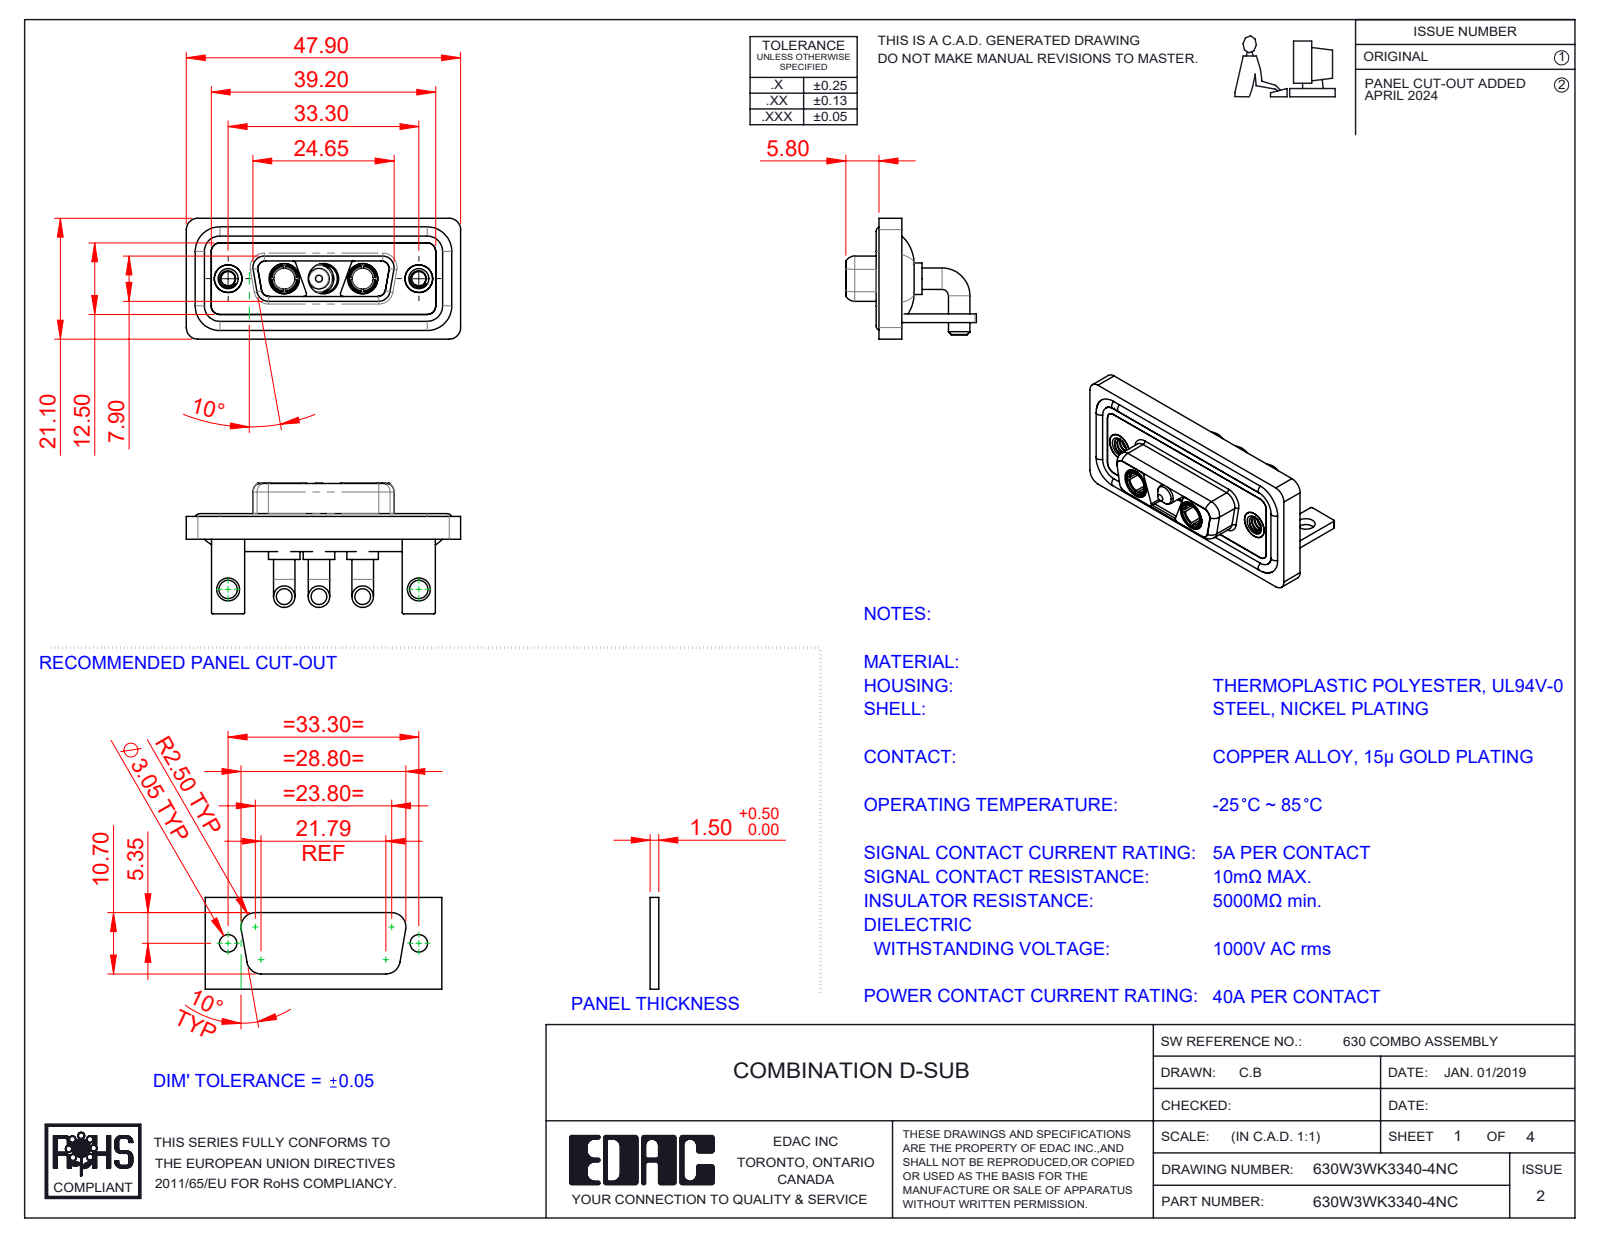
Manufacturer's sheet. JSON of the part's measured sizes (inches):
{"part_name": "630Combo Shell Front_15 Contacts; 630W3WK3340-4NC; 630Combo Waterproof Housing_15 Contacts; 630Combo Threaded Rivet_A (+5 more)", "step_written_by": "SolidWorks 2023 (CONFIG_CONTROL_DESIGN)", "units": "inches", "bodies": {"solids": 15, "faces": 637, "planar": 198, "cylindrical": 286, "other": 153}, "overall_size": [1.886, 0.898, 0.831], "volume_in3": 0.403, "surface_area_in2": 16.44, "round_holes": [[0.191, 5], [0.209, 3], [0.098, 2], [0.126, 2], [0.146, 2], [0.157, 2], [0.159, 2], [0.197, 2]], "round_bosses_or_shafts": [[0.148, 6], [0.063, 4], [0.217, 3], [0.205, 3], [0.187, 3], [0.195, 2], [0.195, 2], [0.189, 2]], "partial_cylinders_radius": [[0.079, 21], [0.059, 18], [0.01, 16], [0.053, 12], [0.02, 9], [0.063, 8], [0.024, 4], [0.026, 4]], "face_to_face_distances": [0.016, 0.114, 0.059, 0.146, 0.071, 0.043, 0.161, 0.063, 0.098, 0.055], "hole_center_spacings": [0.27, 0.386, 0.656, 0.925, 1.311, 0.539]}
